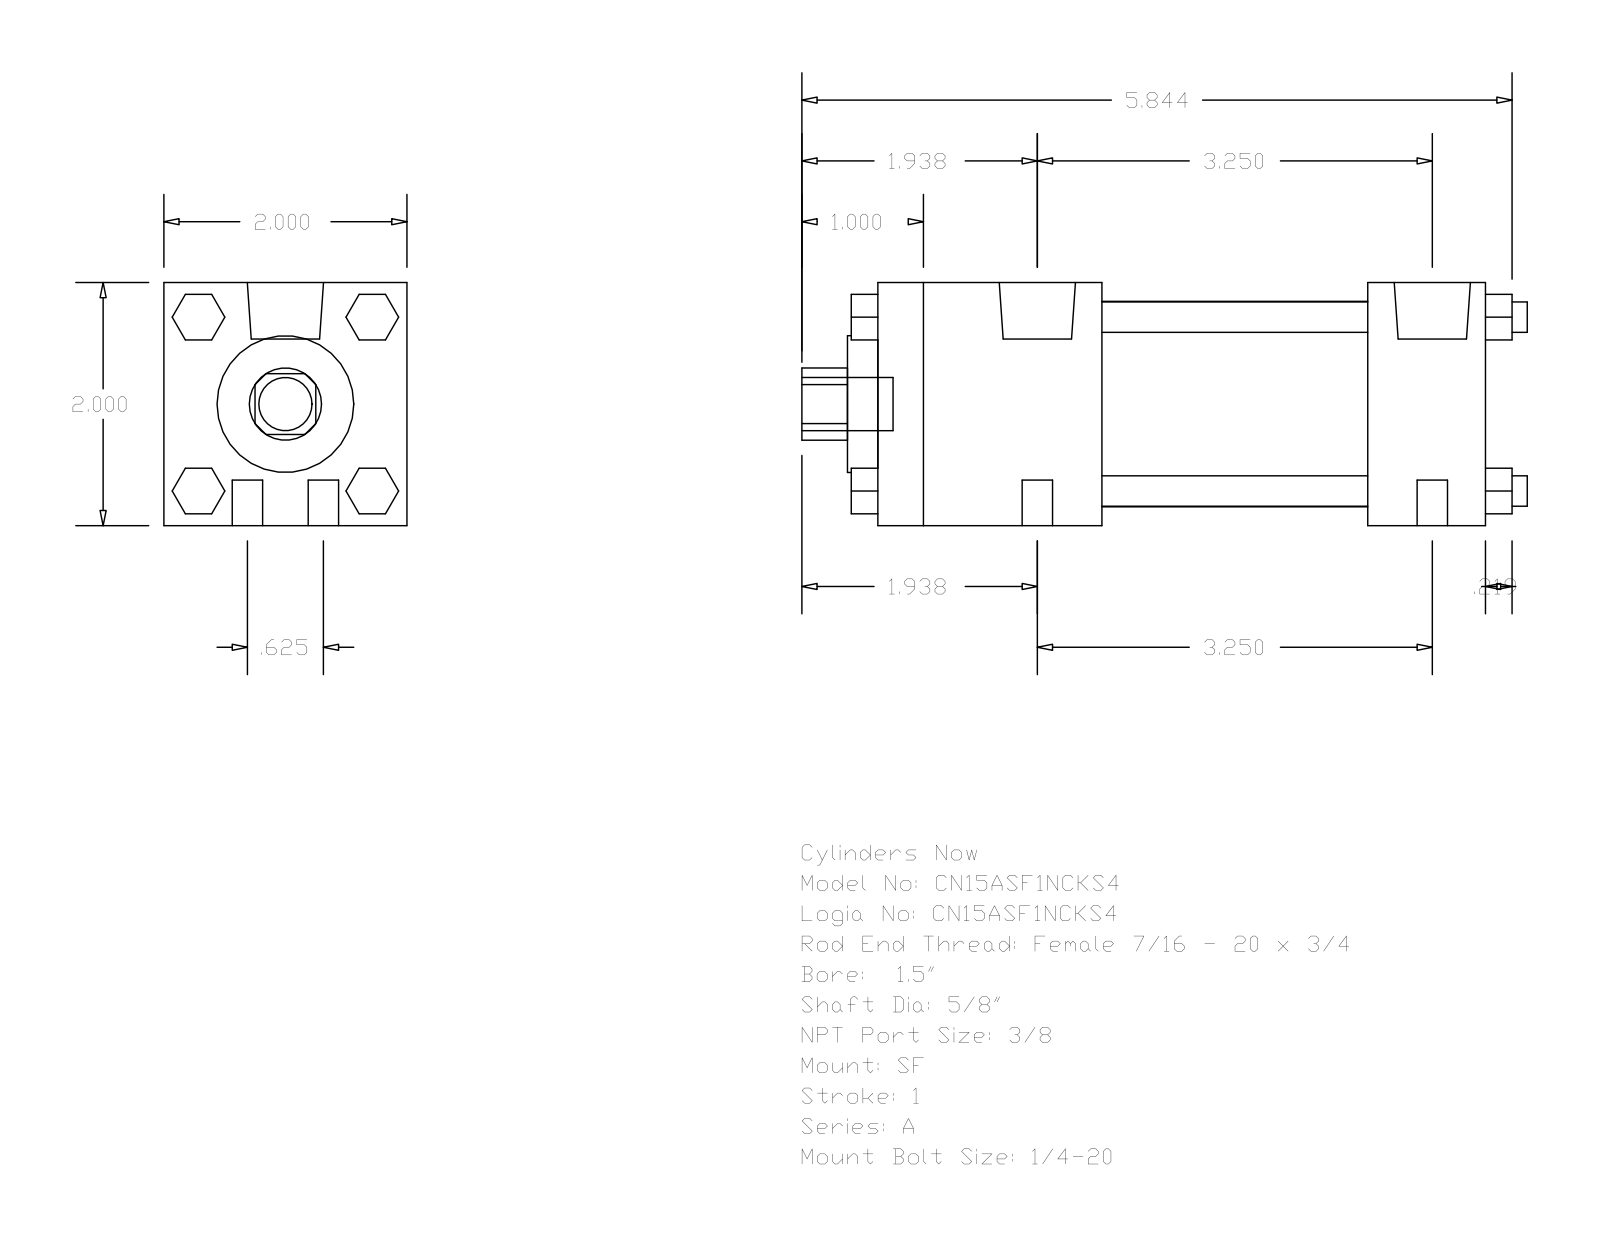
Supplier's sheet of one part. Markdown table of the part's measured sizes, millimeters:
| quantity | value |
| --- | --- |
| part name | A_SF__0150_0.625 |
| STEP written by | GSSL Pune (CONFIG_CONTROL_DESIGN) |
| units | millimeters |
| bodies | 0 solids, 124 faces (94 planar, 30 cylindrical, 0 other) |
| overall size | 151.61 × 50.8 × 50.8 |
| round holes (diameter × count) | 15.88 × 1, 28.57 × 1, 42.93 × 1 |
| round bosses / shafts (diameter × count) | 6.35 × 8, 15.93 × 2, 5.56 × 2, 11.11 × 1 |
| partial cylindrical surfaces (radius × count) | 7.54 × 1 |
| main face-to-face distances | 50.8, 127, 46.83, 102.39, 55.56, 80.17, 24.61, 9.52, 6.35, 53.18 |
